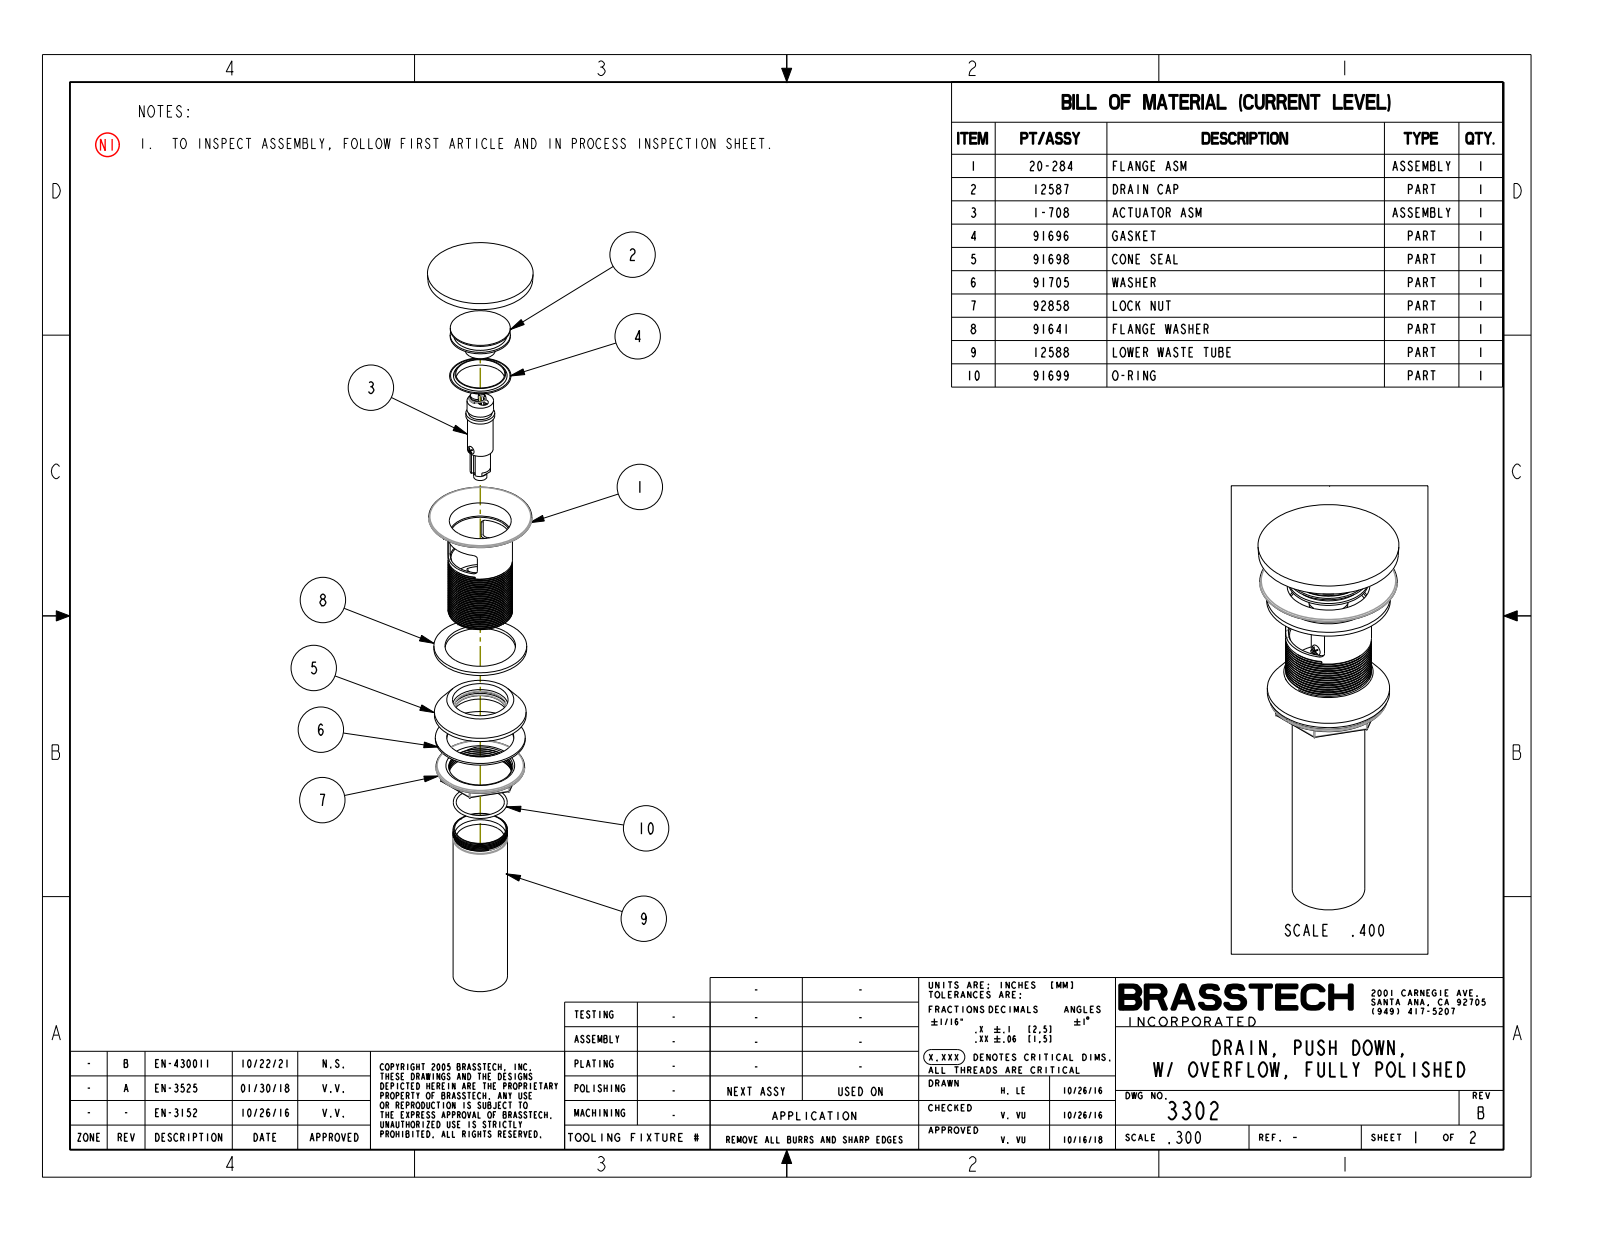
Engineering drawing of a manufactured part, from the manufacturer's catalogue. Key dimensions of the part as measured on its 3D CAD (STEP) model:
Part name (STEP PRODUCT): 3302
STEP written by: CREO PARAMETRIC BY PTC INC, 2018500 (CONFIG_CONTROL_DESIGN)
Units: inches
Bodies: 3 solids, 317 faces (62 planar, 148 cylindrical, 107 other)
Overall size (bounding box): 7.012 × 2.362 × 2.362
Volume: 7.379 in³ · Surface area: 102.7 in²
Round holes (diameter × count): ⌀1.176 ×1, ⌀1.181 ×1, ⌀1.228 ×1, ⌀1.28 ×1, ⌀1.339 ×1, ⌀1.378 ×1, ⌀1.417 ×1, ⌀1.44 ×1, ⌀1.535 ×1, ⌀1.614 ×1
Round bosses / shafts (diameter × count): ⌀0.05 ×3, ⌀2.362 ×1, ⌀2.126 ×1, ⌀2.1 ×1, ⌀2.059 ×1, ⌀2.028 ×1, ⌀1.476 ×1, ⌀1.376 ×1
Partial cylindrical surfaces — rounded edges, fillets, slot ends (radius × count): R0.02 ×18, R0.059 ×4, R0.079 ×4
Main face-to-face distances: 1.42, 0.158, 0.591, 0.908, 1.341, 0.079, 0.047, 0.205, 1.546, 1.625
